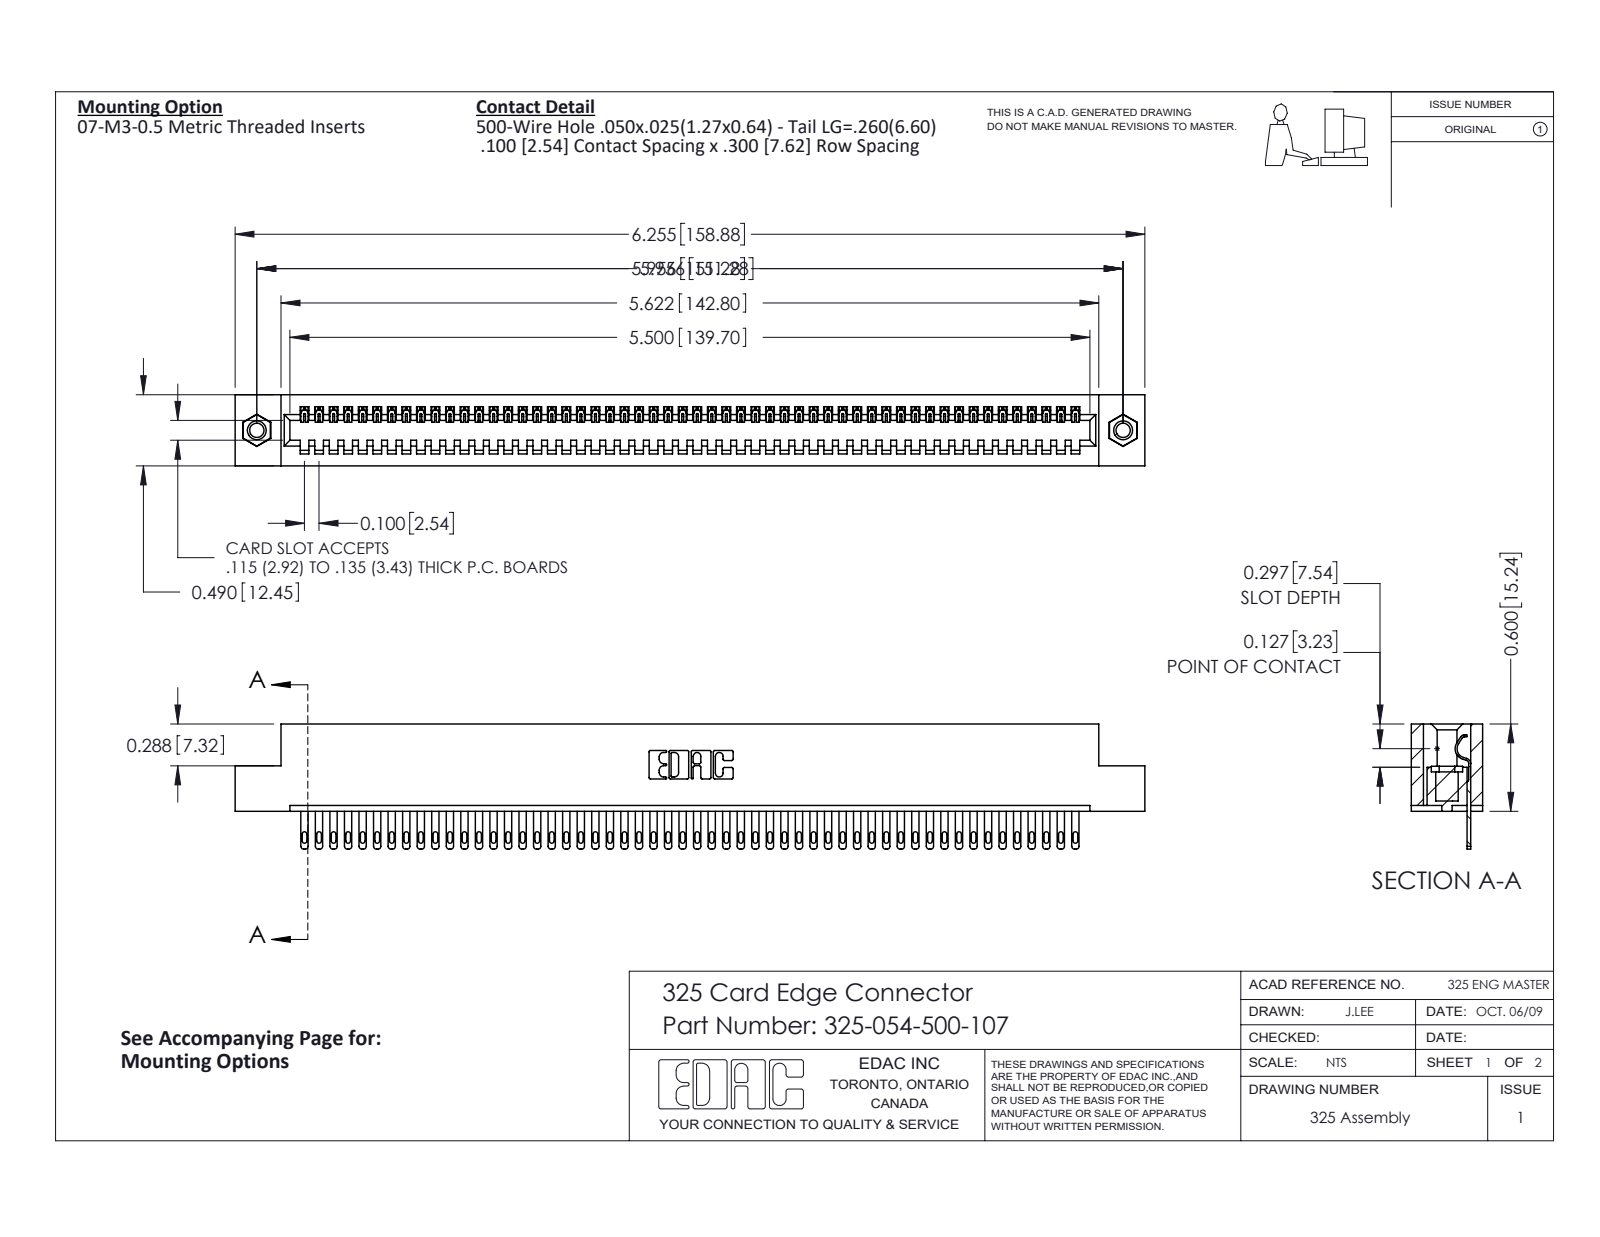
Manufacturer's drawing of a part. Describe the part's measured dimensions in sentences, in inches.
The part is named "325-054-500-107; 345-250-001_345-250-005-103; 325-292-001_325-293-100; 325 Part_TI". Its 3-D file was written by "SolidWorks 2016 (CONFIG_CONTROL_DESIGN)". It is 57 solids with 3090 faces: 2046 planar, 1028 cylindrical and 16 other. Overall it measures 6.255 by 0.86 by 0.49 inches. Its volume is 1.238 cubic inches and its surface area 34.9 square inches. Round holes: 2 of diameter 0.098, 2 of diameter 0.125, 2 of diameter 0.16. Round bosses or shafts: 2 of diameter 0.155. Partial cylindrical surfaces (rounded edges, fillets, slot ends): 108 of radius 0.006, 108 of radius 0.016, 108 of radius 0.02, 22 of radius 0.01, 6 of radius 0.007, 6 of radius 0.031, 3 of radius 0.026, 1 of radius 0.014. The main face-to-face distances are 0.083, 0.407, 0.3, 0.49, 0.107, 0.383, 0.025, 0.325, 0.56, 0.263. The hole center spacings are 5.956.
